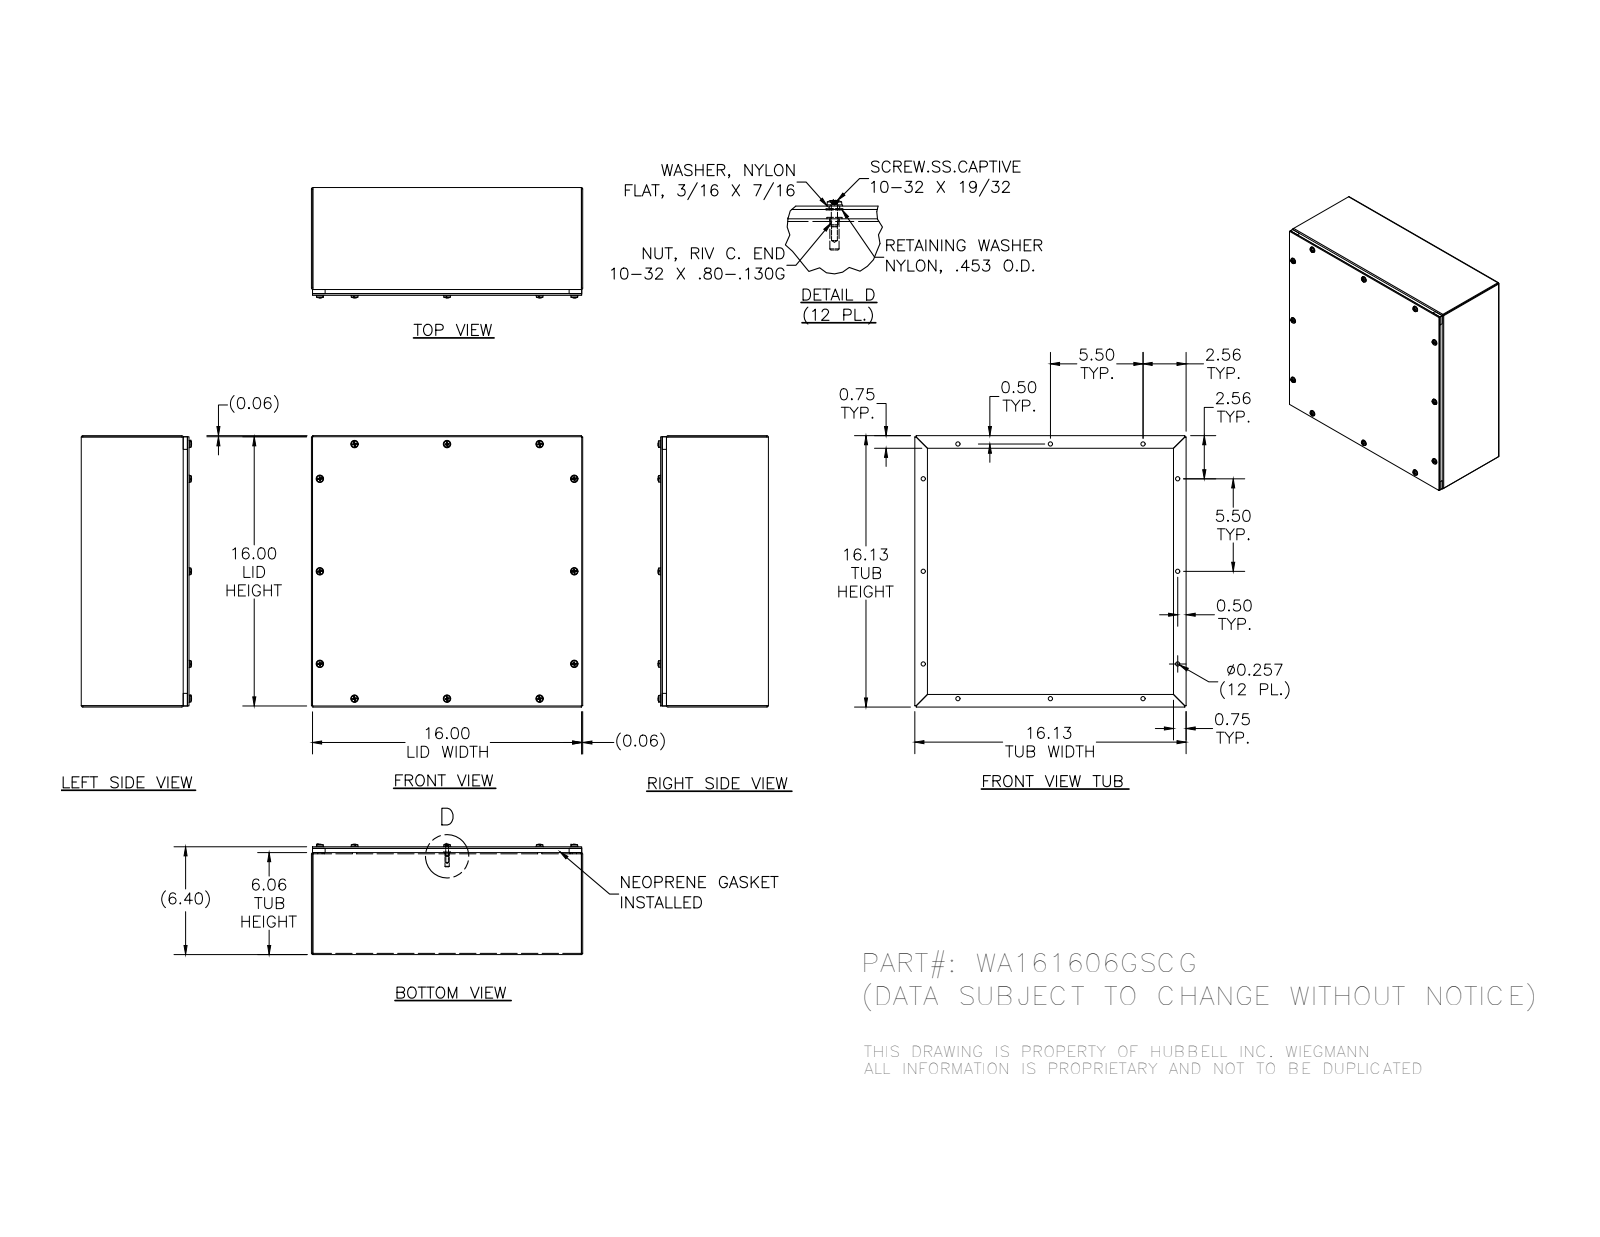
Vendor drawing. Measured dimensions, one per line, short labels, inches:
name: 37210; WA161606GSCG; 39035; WA161606GSCGBKP (+3 more)
written by: SolidWorks 2014 (AUTOMOTIVE_DESIGN)
unit: in
bodies: 54 solids, 1264 faces (596 planar, 328 cylindrical, 340 other)
size: 16.125 × 16.125 × 6.558
volume: 87 in³; area: 2 048 in²
holes: 12× ⌀0.156, 12× ⌀0.188, 12× ⌀0.196, 12× ⌀0.257, 12× ⌀0.278, 12× ⌀0.281
bosses: 12× ⌀0.453, 12× ⌀0.437, 12× ⌀0.406, 12× ⌀0.248, 12× ⌀0.167
rounds: 12× R0.089, 8× R0.016, 8× R0.09
face distances: 0.074, 0.094, 6.33, 6.404, 6.236, 6.31, 0.074, 15.977, 16.051, 16.125
hole spacings: 5.5, 16.094, 11, 15.093, 15.125, 13.224, 7.838, 7.839
